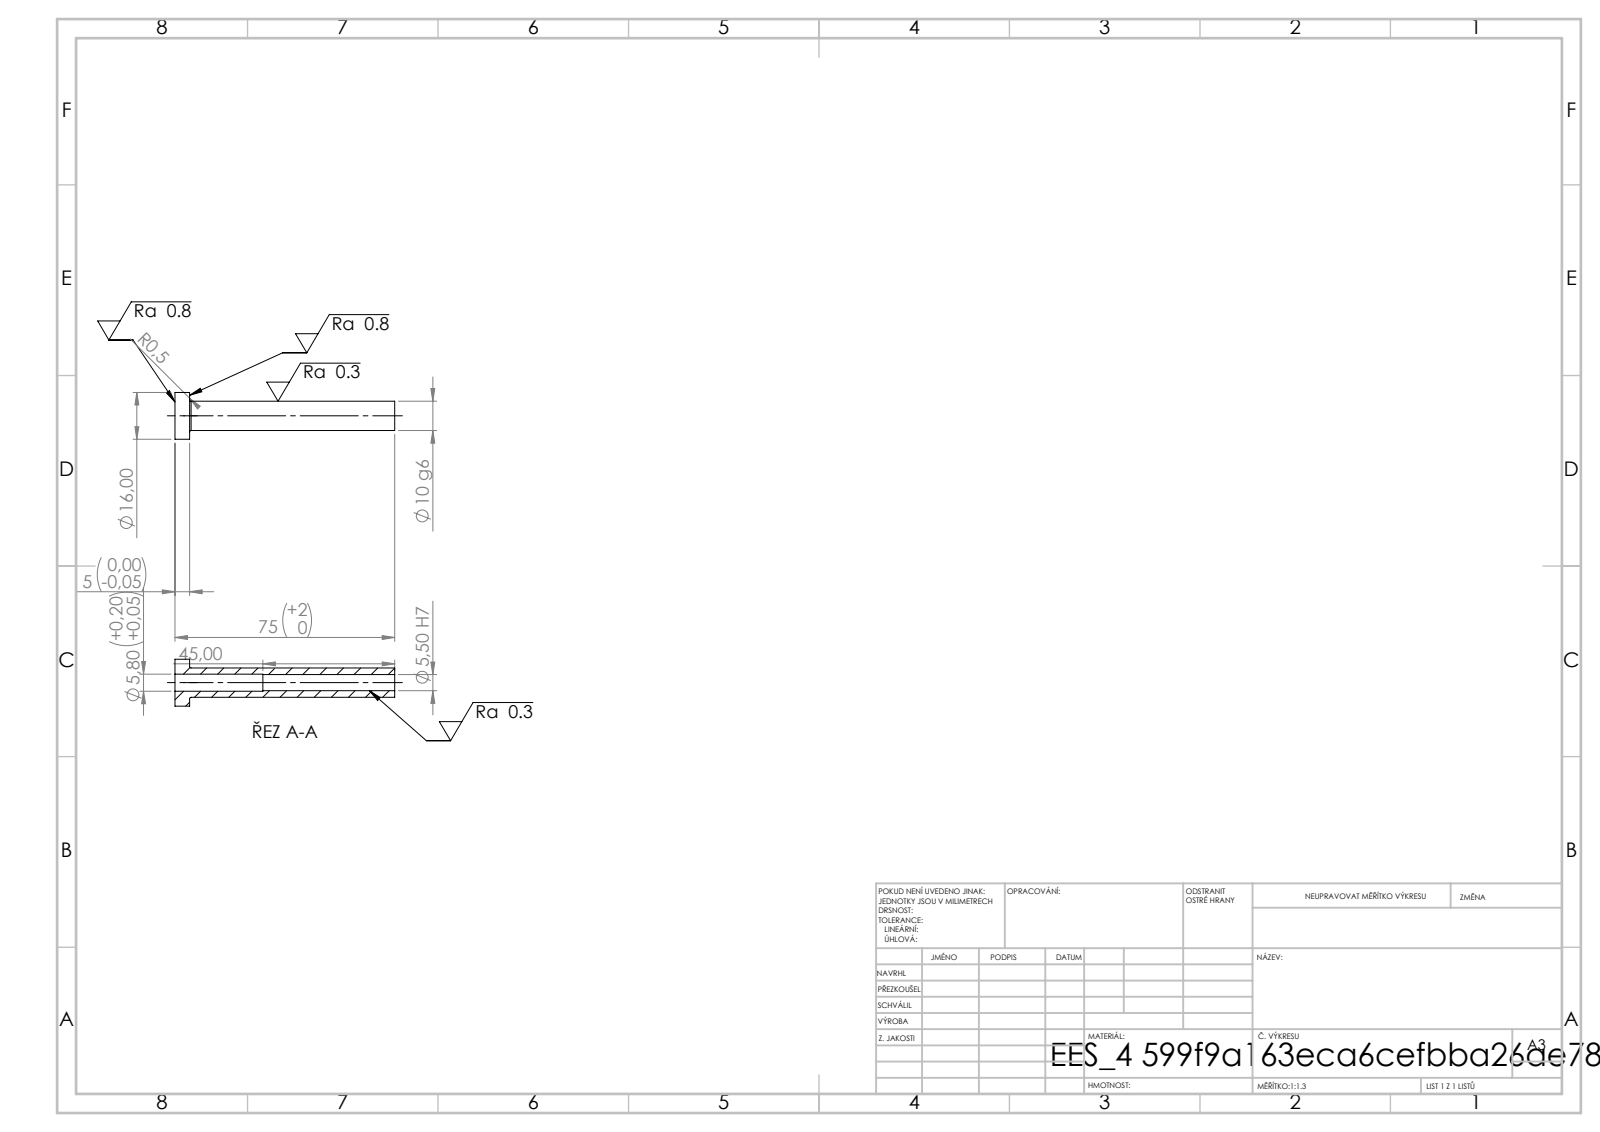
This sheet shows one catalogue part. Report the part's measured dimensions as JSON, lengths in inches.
{"step_written_by": "SolidWorks 2019 (CONFIG_CONTROL_DESIGN)", "units": "inches", "bodies": {"solids": 1, "faces": 14, "planar": 4, "cylindrical": 8, "other": 2}, "overall_size": [2.953, 0.63, 0.63], "volume_in3": 0.283, "surface_area_in2": 6.391, "round_holes": [[0.217, 1], [0.228, 1]], "round_bosses_or_shafts": [[0.63, 1], [0.394, 1]], "face_to_face_distances": [0.197, 2.953, 2.756, 1.181, 0.984, 1.772]}
